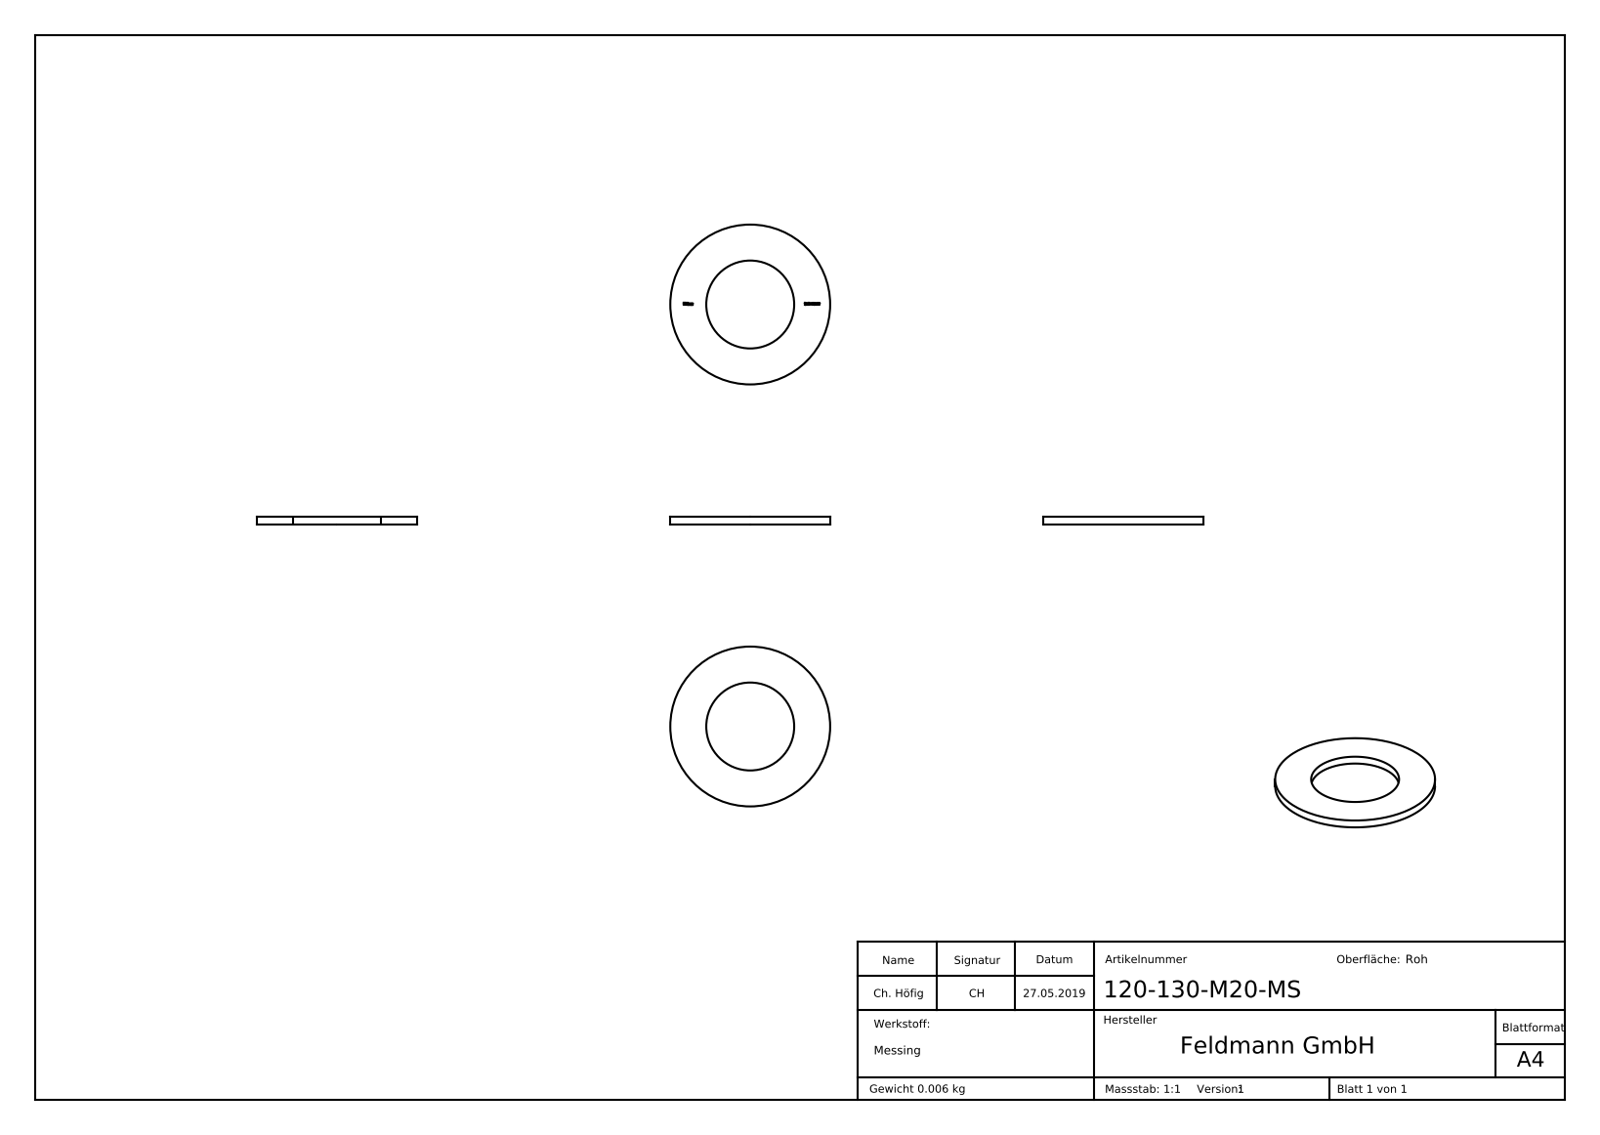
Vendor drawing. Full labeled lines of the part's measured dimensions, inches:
Part name (STEP PRODUCT): 120-130-M20-MS
STEP written by: SolidWorks 2015 (CONFIG_CONTROL_DESIGN)
Units: inches
Bodies: 1 solid, 271 faces (151 planar, 4 cylindrical, 116 other)
Overall size (bounding box): 1.181 × 1.181 × 0.059
Volume: 0.045 in³ · Surface area: 1.872 in²
Round holes (diameter × count): ⌀0.65 ×1
Round bosses / shafts (diameter × count): ⌀1.181 ×1
Main face-to-face distances: 0.059, 0.055, 0.034, 0.029, 0.033, 0.03, 0.881, 0.909, 0.023, 0.898
